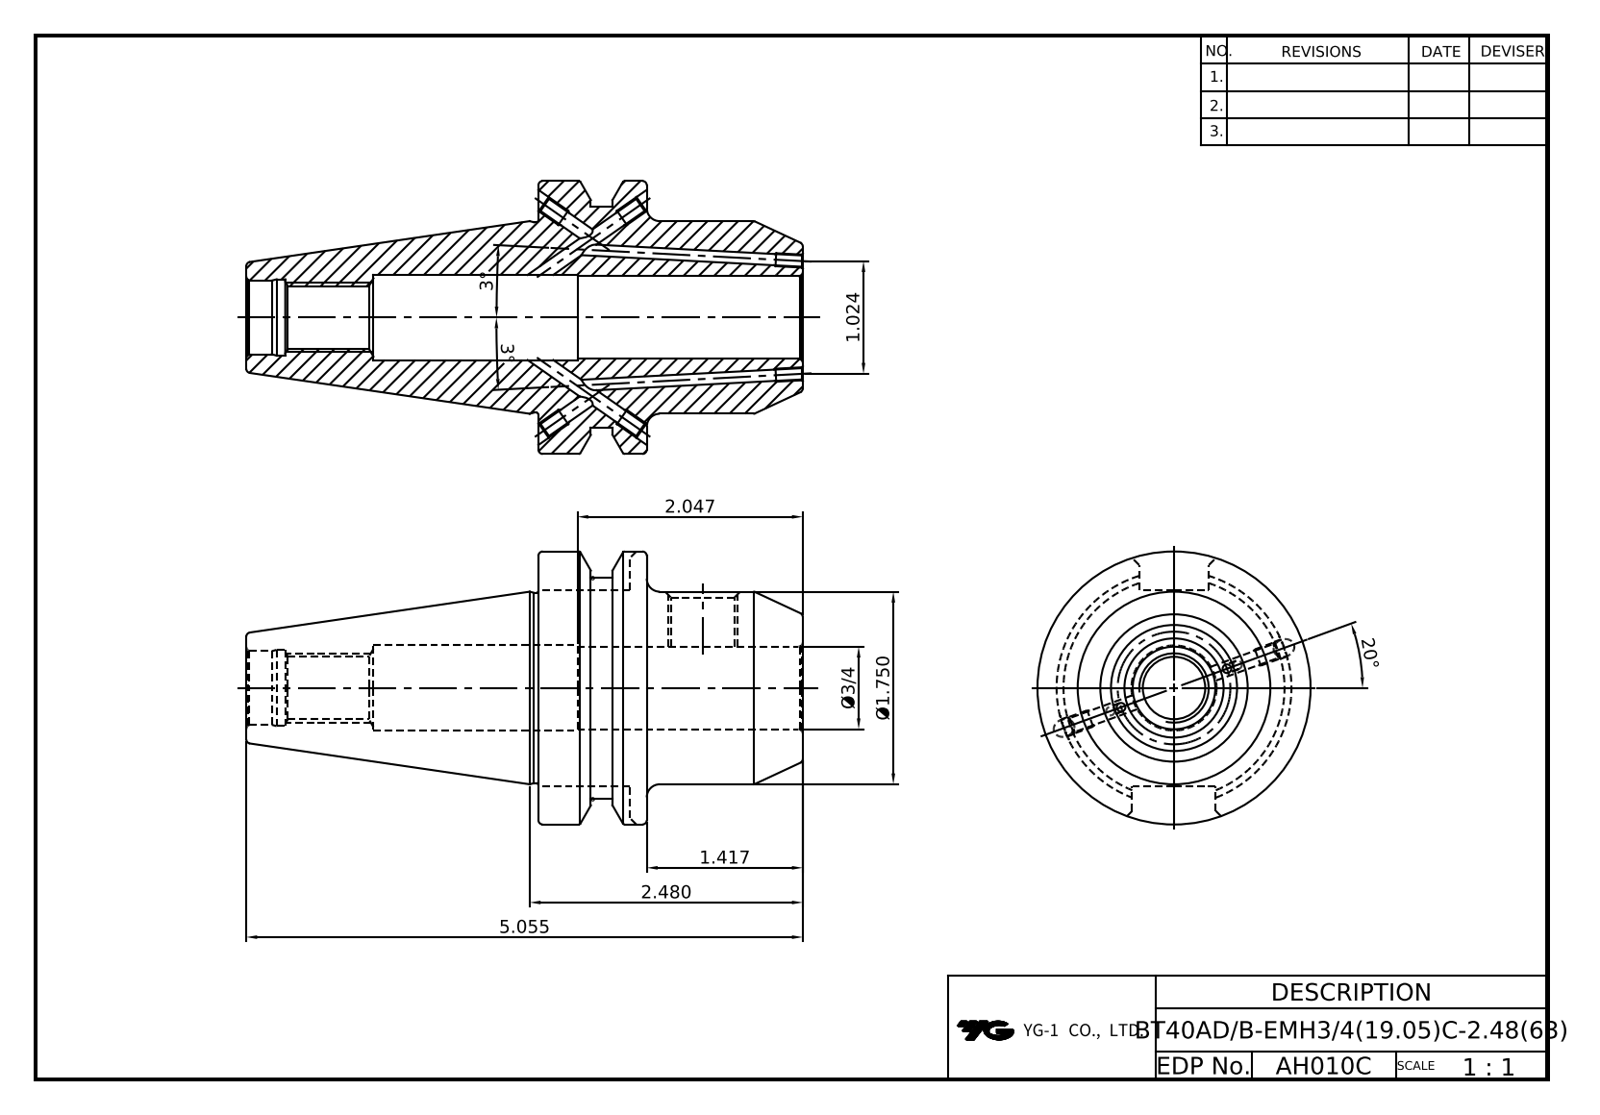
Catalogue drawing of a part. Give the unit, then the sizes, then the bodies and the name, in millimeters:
Units: millimetres
Overall size (bounding box): 128.4 × 63 × 63
Round holes (diameter × count): ⌀4 ×6, ⌀3.4 ×4, ⌀2.5 ×2, ⌀3 ×2, ⌀14 ×1, ⌀14.27 ×1, ⌀15.88 ×1, ⌀16 ×1, ⌀17 ×1, ⌀17.6 ×1, ⌀19.05 ×1, ⌀19.65 ×1
Round bosses / shafts (diameter × count): ⌀63 ×1, ⌀51 ×1, ⌀44.45 ×1, ⌀44 ×1
Partial cylindrical surfaces — rounded edges, fillets, slot ends (radius × count): R8.05 ×1
Main face-to-face distances: 25, 61, 36, 45.2, 17.1, 7.9, 43.9, 12.1, 5, 12.9
Hole centre spacings: 29.89, 29.9
Volume: 147 318 mm³ · Surface area: 34 248 mm²
Bodies: 1 solid, 146 faces (39 planar, 60 cylindrical, 47 other)
Part name (STEP PRODUCT): BT40ADB_EMH19_05C_63
STEP written by: CREO PARAMETRIC BY PTC INC, 2018100 (CONFIG_CONTROL_DESIGN)
